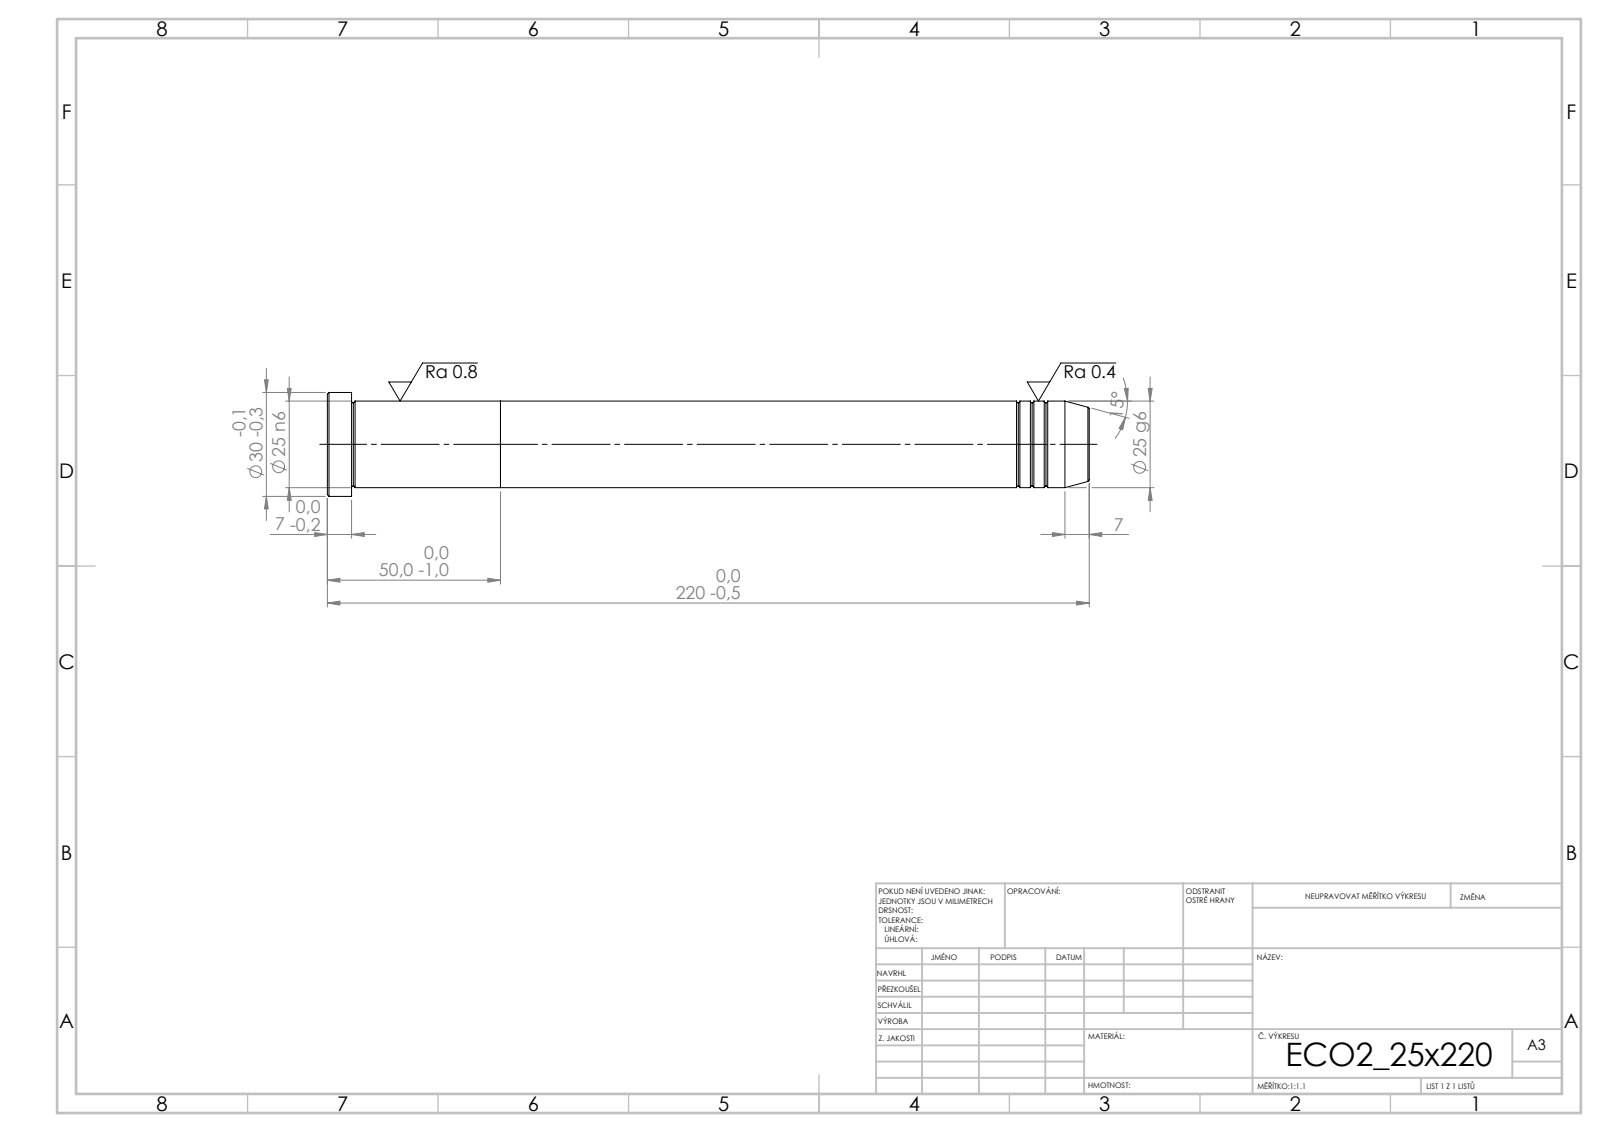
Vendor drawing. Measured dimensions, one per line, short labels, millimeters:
written by: SolidWorks 2019 (CONFIG_CONTROL_DESIGN)
unit: mm
bodies: 2 solids, 39 faces (5 planar, 12 cylindrical, 22 other)
size: 220 × 30 × 30
volume: 108 880 mm³; area: 19 756 mm²
bosses: 1× ⌀30, 1× ⌀25
face distances: 50, 170, 220, 213, 43, 7
